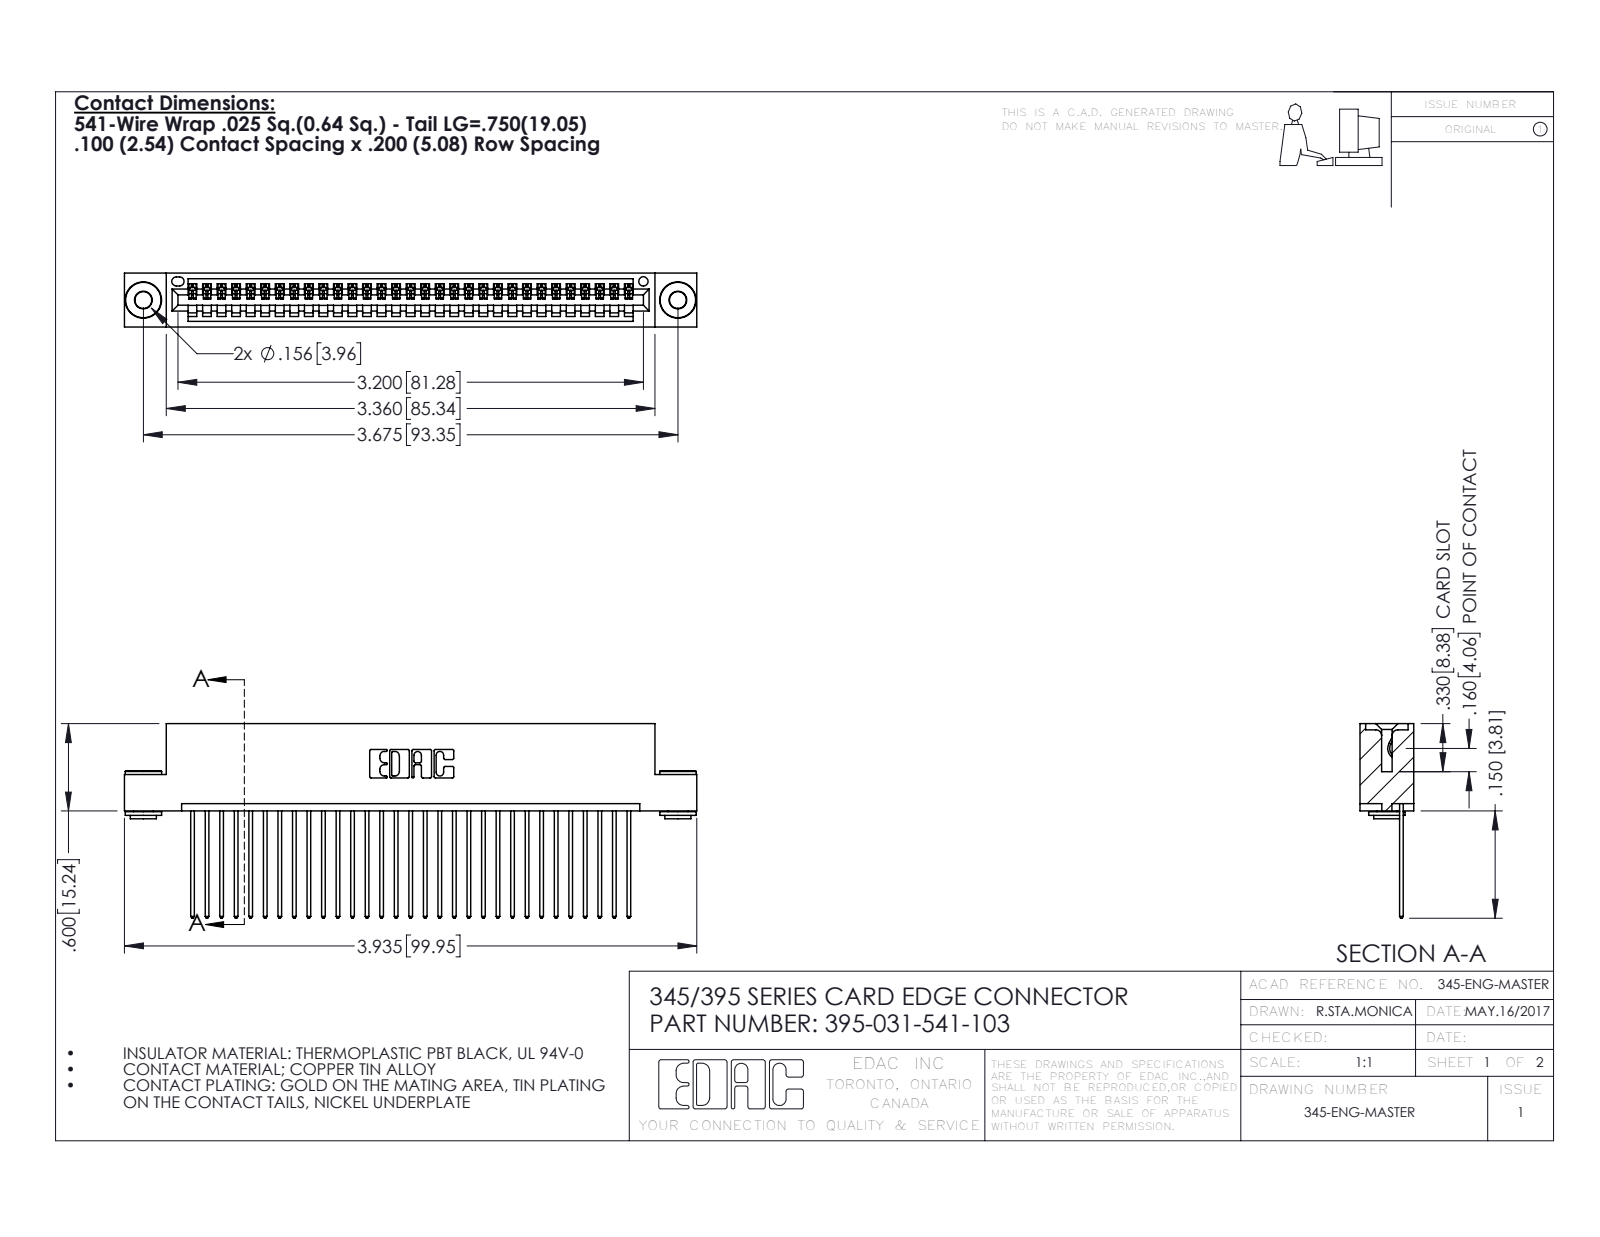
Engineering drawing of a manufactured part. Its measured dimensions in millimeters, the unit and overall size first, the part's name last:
Units: millimetres
Overall size (bounding box): 99.9 × 34 × 9.4
Round holes (diameter × count): ⌀2.9 ×2, ⌀4 ×2, ⌀1.6 ×1
Round bosses / shafts (diameter × count): ⌀6.4 ×2, ⌀4.6 ×2, ⌀3.5 ×2
Partial cylindrical surfaces — rounded edges, fillets, slot ends (radius × count): R0.2 ×62, R0.3 ×62, R0.3 ×22, R0.2 ×6, R0.8 ×6, R0.7 ×3, R0.8 ×2, R1 ×2
Main face-to-face distances: 1.8, 7.6, 5.1, 0.6, 9.4, 2.5, 6.9, 5.7, 3.8, 1.8
Hole centre spacings: 6.9, 87.4, 93.3
Volume: 9 520 mm³ · Surface area: 13 320 mm²
Bodies: 34 solids, 1962 faces (1330 planar, 624 cylindrical, 8 other)
Part name (STEP PRODUCT): 345 Part_Flush Mounting Lugs - 0.156 Dia-TH; 395-031-541-103; 345-250-002_345-250-002-102; 345-292-001_345-293-141
STEP written by: SolidWorks 2016 (CONFIG_CONTROL_DESIGN)
